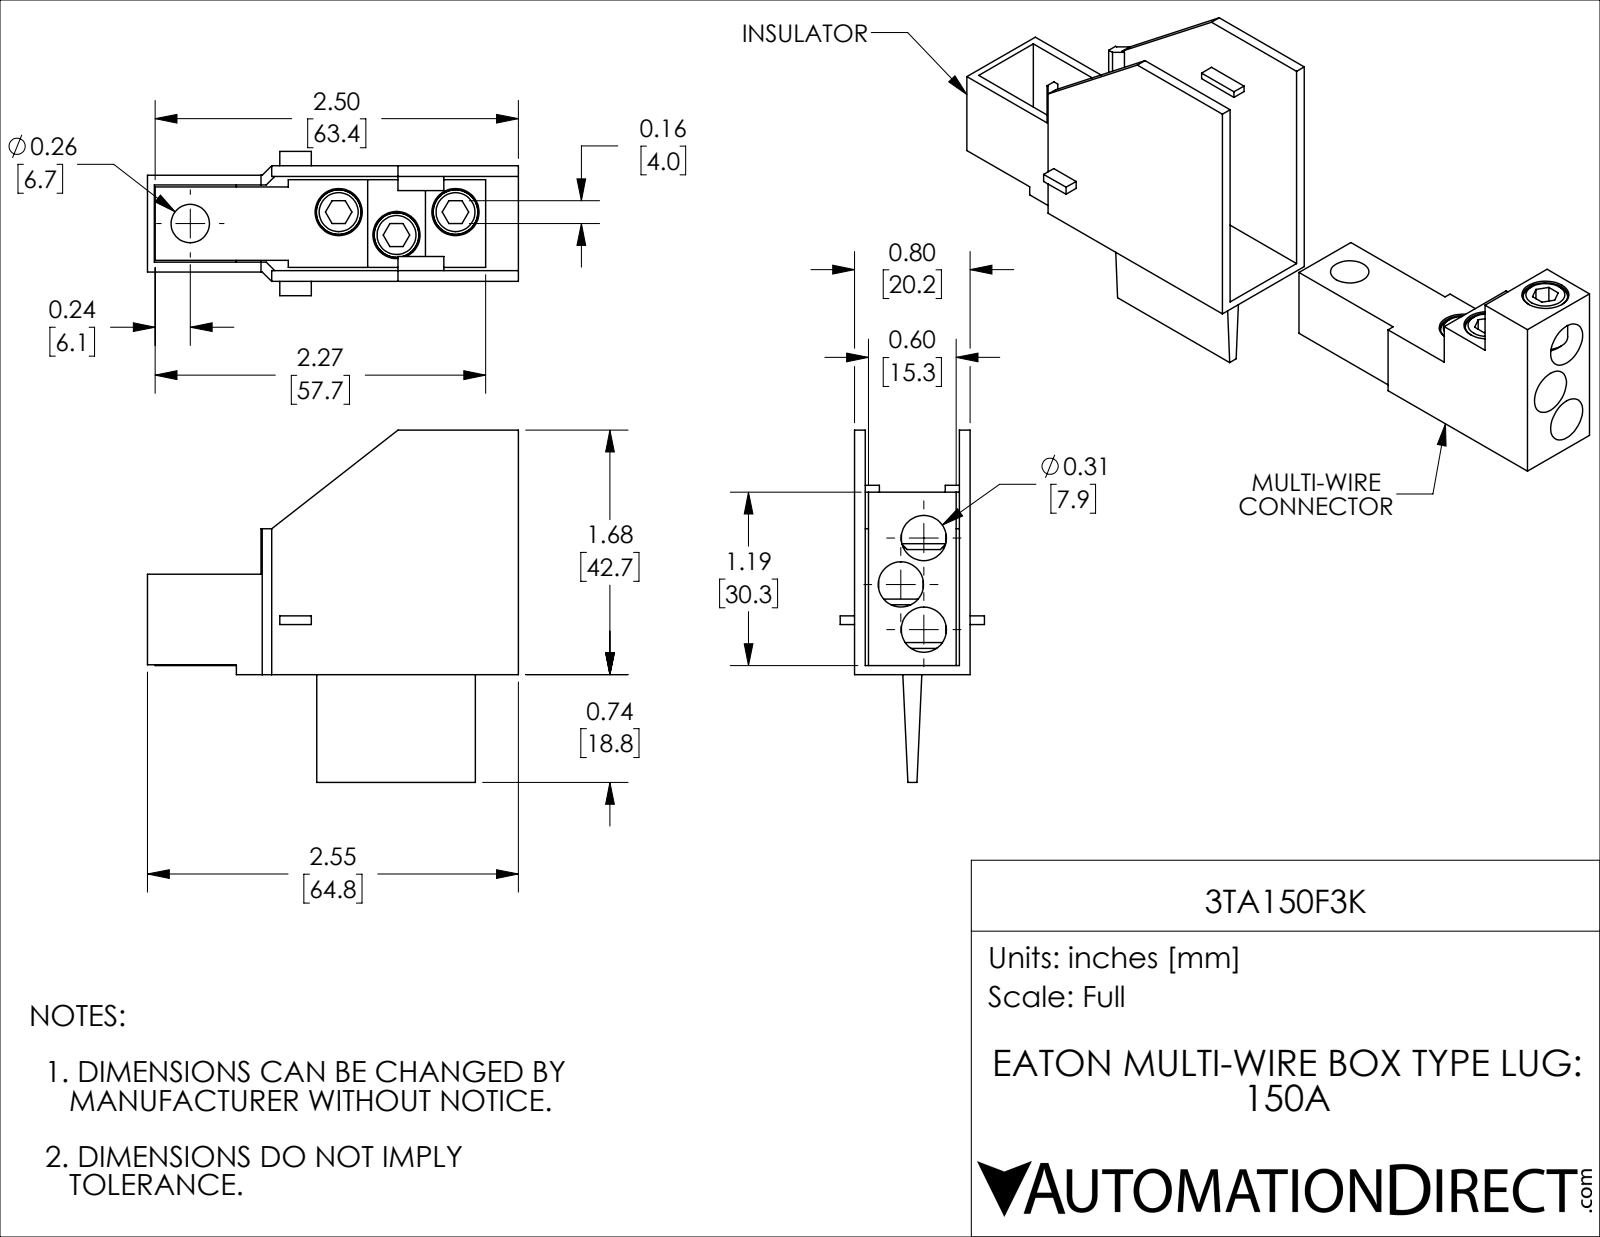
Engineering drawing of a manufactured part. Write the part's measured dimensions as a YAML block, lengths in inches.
part_name: "3TA150F3K"
step_written_by: "SolidWorks 2019 (CONFIG_CONTROL_DESIGN)"
units: inches
bodies: {solids: 5, faces: 135, planar: 97, cylindrical: 20, other: 18}
overall_size: [2.549, 2.421, 0.992]
volume: 1.335
surface_area: 30.38
round_holes:
  - {diameter: 0.308, count: 3}
  - {diameter: 0.311, count: 3}
  - {diameter: 0.264, count: 1}
round_bosses_or_shafts:
  - {diameter: 0.307, count: 3}
face_to_face_distances: [0.074, 0.721, 0.795, 0.647, 0.096, 0.699, 0.022, 0.625, 0.063, 0.067]
hole_center_spacings: [0.348, 0.355, 0.428, 0.435, 0.63, 0.803, 1.024, 1.42]
